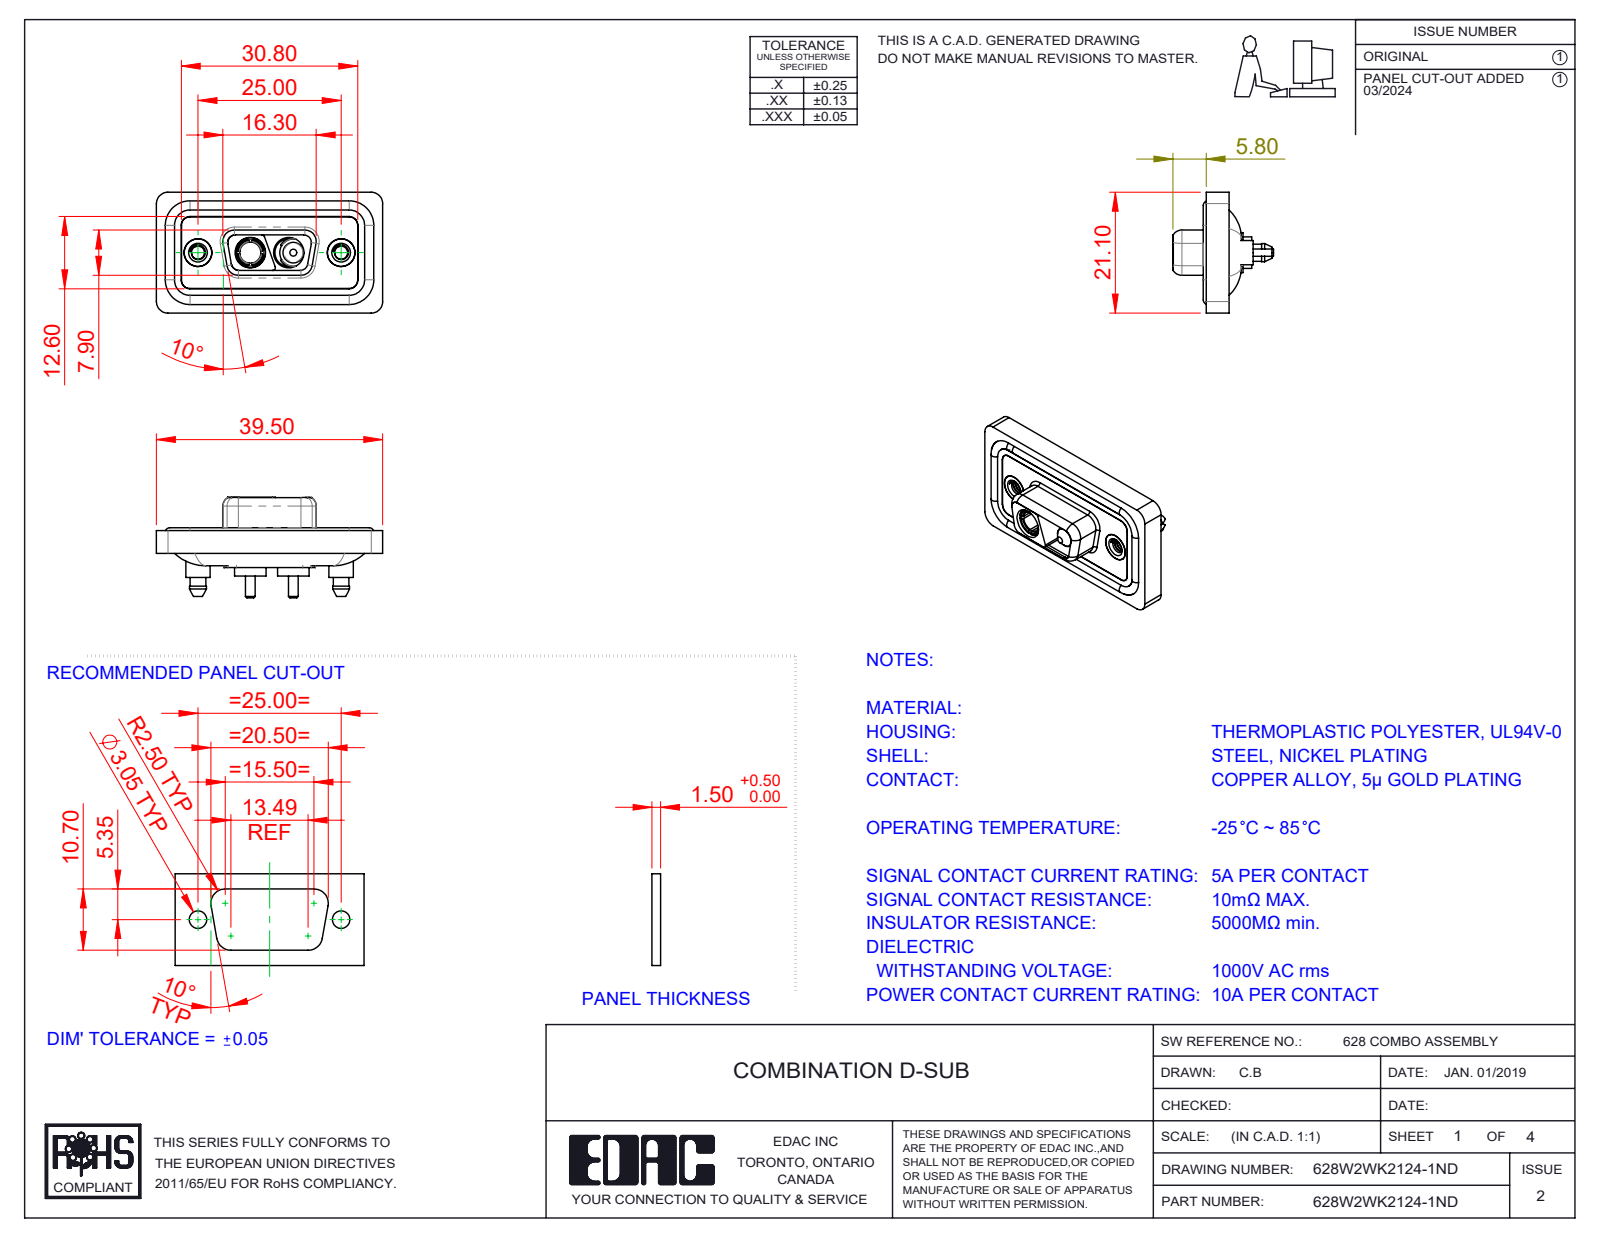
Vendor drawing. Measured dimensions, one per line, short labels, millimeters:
name: 628Combo Waterproof Housing_09 Contacts; 628Combo Shell Front_09 Contacts; Power Pin_10A S; 628W2WK2124-1ND (+4 more)
written by: SolidWorks 2023 (CONFIG_CONTROL_DESIGN)
unit: mm
bodies: 11 solids, 566 faces (160 planar, 279 cylindrical, 127 other)
size: 39.5 × 21.1 × 17.55
volume: 4 709 mm³; area: 7 658 mm²
holes: 4× ⌀4.85, 2× ⌀2.26, 2× ⌀4, 2× ⌀4.05, 2× ⌀5, 2× ⌀5.3, 1× ⌀3.7
bosses: 4× ⌀1.6, 2× ⌀5.5, 2× ⌀5.4, 2× ⌀5.2, 2× ⌀4.95, 2× ⌀4.8, 2× ⌀4.75, 2× ⌀4.25
rounds: 24× R1.5, 18× R2, 10× R1.6, 8× R1.35, 6× R0.5, 4× R0.25, 4× R0.6, 4× R0.65
face distances: 0.4, 1.1, 2.9, 1.6, 0.5, 1.8, 5.65, 1.5, 4, 5.35
hole spacings: 9.14, 15.86, 6.72, 25
